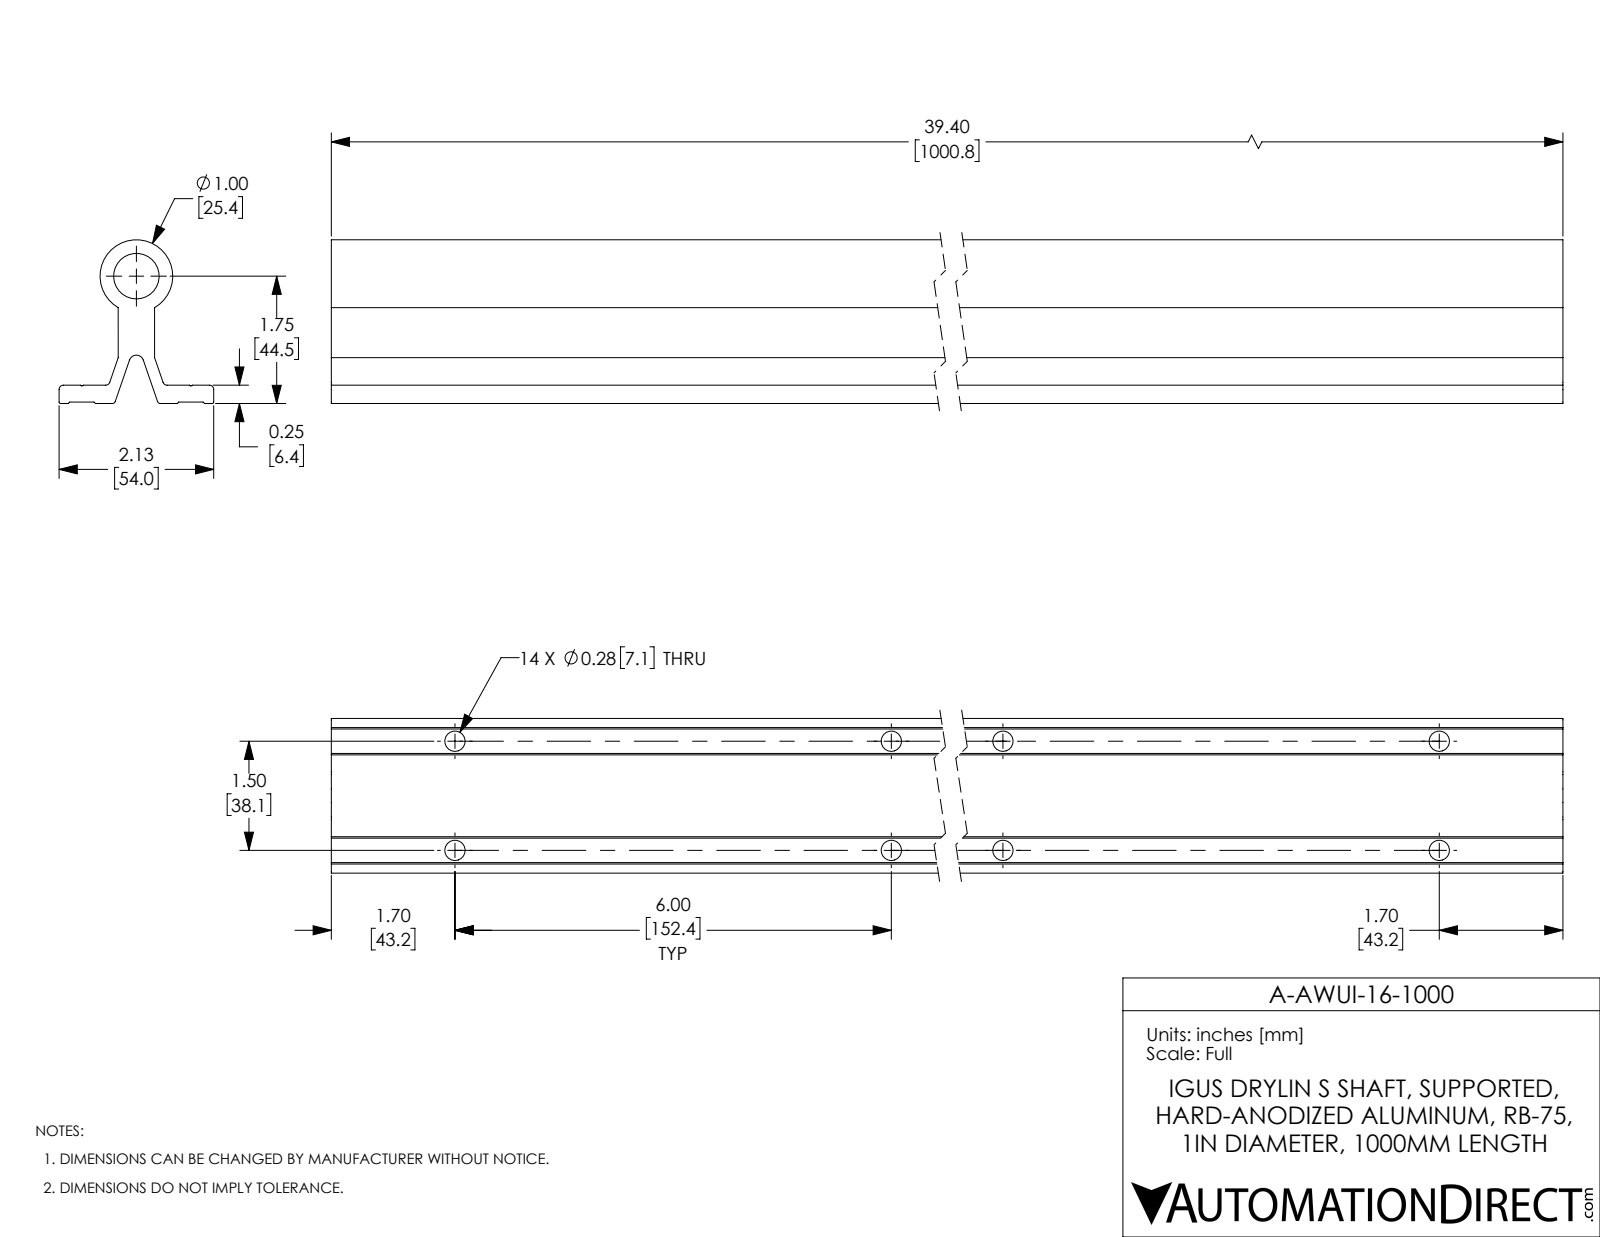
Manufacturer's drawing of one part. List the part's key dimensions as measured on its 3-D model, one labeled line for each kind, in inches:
Part name (STEP PRODUCT): A-AWUI-16-1000
STEP written by: SolidWorks 2017 (AUTOMOTIVE_DESIGN)
Units: inches
Bodies: 1 solid, 96 faces (56 planar, 40 cylindrical, 0 other)
Overall size (bounding box): 39.4 × 2.25 × 2.126
Volume: 51.47 in³ · Surface area: 461 in²
Round holes (diameter × count): ⌀0.28 ×14, ⌀0.626 ×1
Round bosses / shafts (diameter × count): ⌀1 ×1
Partial cylindrical surfaces — rounded edges, fillets, slot ends (radius × count): R0.059 ×4, R0.02 ×2, R0.039 ×2, R0.1 ×1
Main face-to-face distances: 0.157, 0.252, 0.02, 0.232, 0.813, 2.126, 1.313, 1.061, 0.75, 39.4
Hole centre spacings: 6, 6.185, 12, 12.093, 18, 18.062, 1.5, 24
